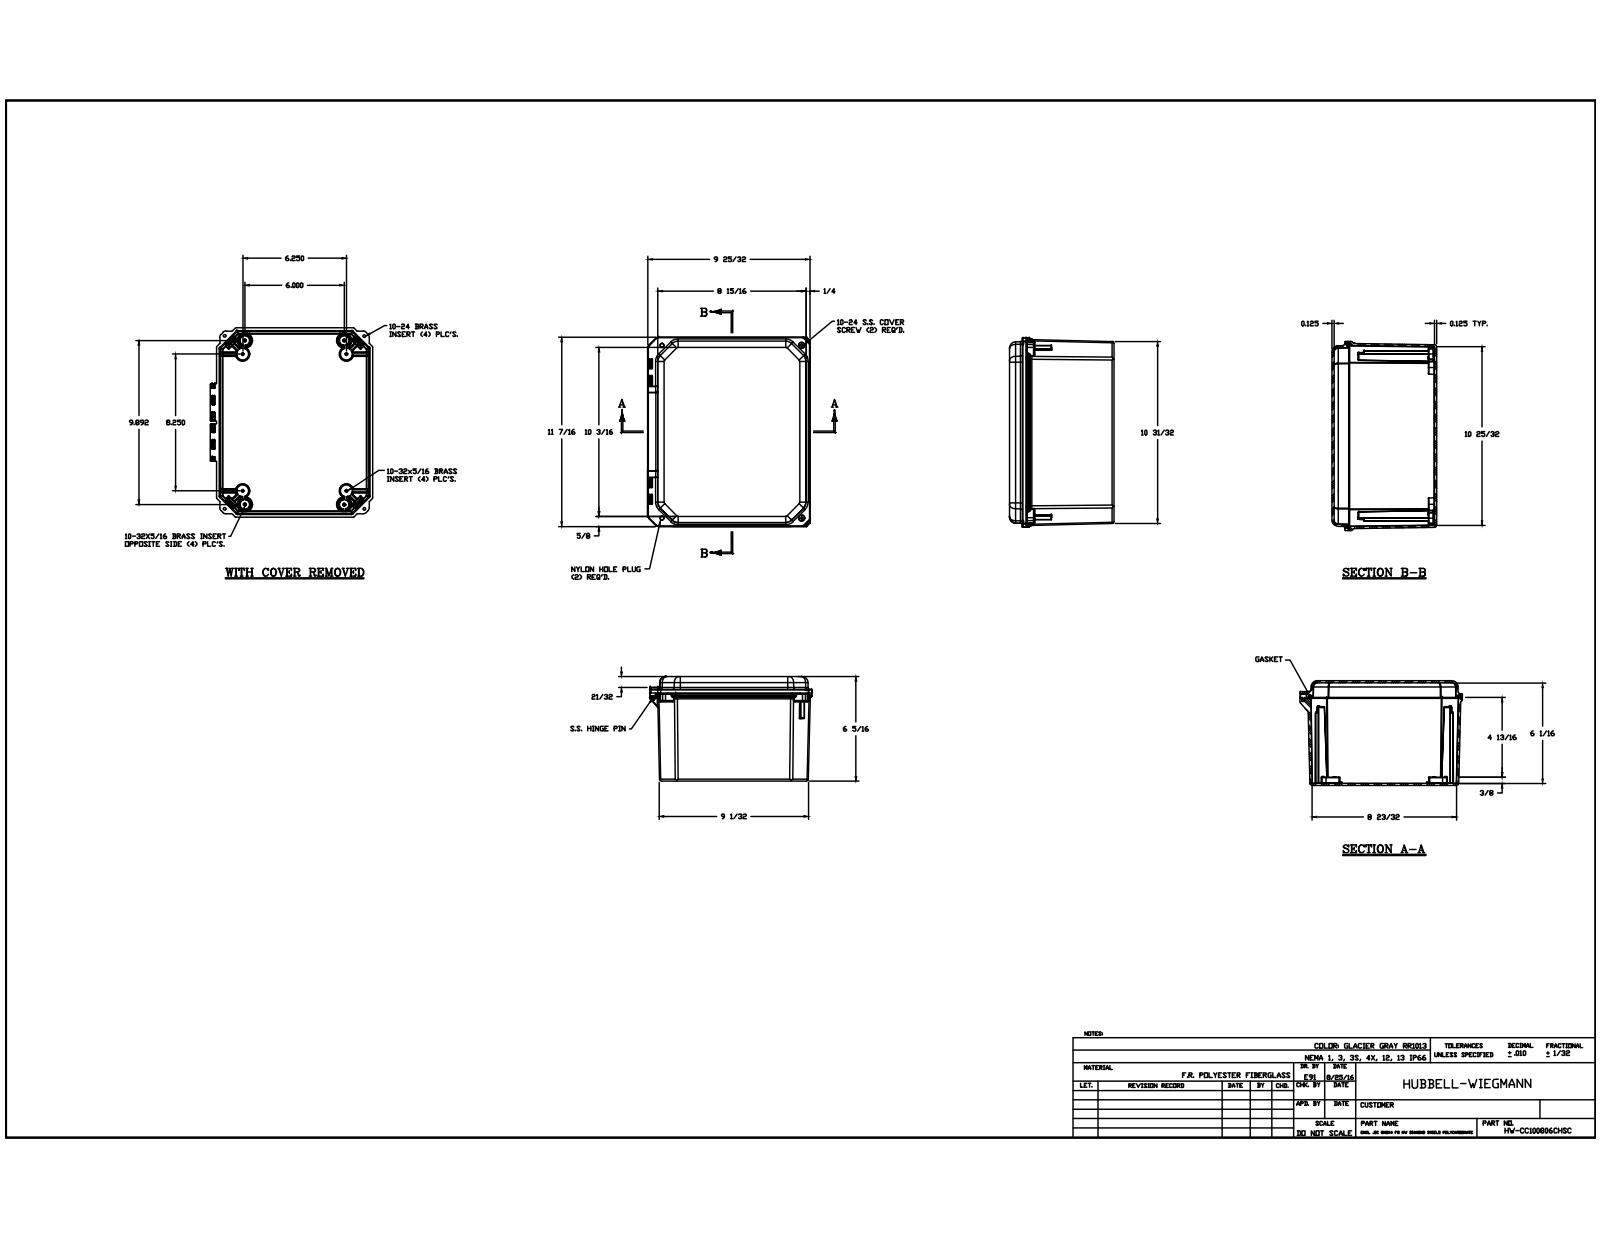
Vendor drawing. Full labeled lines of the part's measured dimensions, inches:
Part name (STEP PRODUCT): HW-CC100806CHSC; DS100806BOX; BRASS INSERT-(; BRASS INSERT-(_1 (+7 more)
STEP written by: Autodesk Inventor 2017 (CONFIG_CONTROL_DESIGN)
Units: inches
Bodies: 23 solids, 2014 faces (546 planar, 754 cylindrical, 714 other)
Overall size (bounding box): 11.424 × 9.801 × 6.312
Volume: 62.79 in³ · Surface area: 954.4 in²
Round holes (diameter × count): ⌀0.156 ×12, ⌀0.152 ×8, ⌀0.219 ×4, ⌀0.252 ×4, ⌀0.312 ×4, ⌀0.15 ×2, ⌀0.137 ×1
Round bosses / shafts (diameter × count): ⌀0.246 ×12, ⌀0.87 ×4, ⌀0.45 ×2, ⌀0.209 ×2, ⌀0.199 ×2, ⌀0.135 ×1
Partial cylindrical surfaces — rounded edges, fillets, slot ends (radius × count): R0.01 ×188, R0.005 ×94, R0.02 ×59, R0.03 ×37, R0.125 ×29, R0.03 ×24, R0.09 ×24, R0.25 ×24
Main face-to-face distances: 0.125, 6.187, 0.127, 0.126, 6.312, 6.062, 0.25, 5.531, 0.656, 1
Hole centre spacings: 0.831, 8.25, 9.072, 9.399, 11.873, 10.35, 1.24, 1.536
